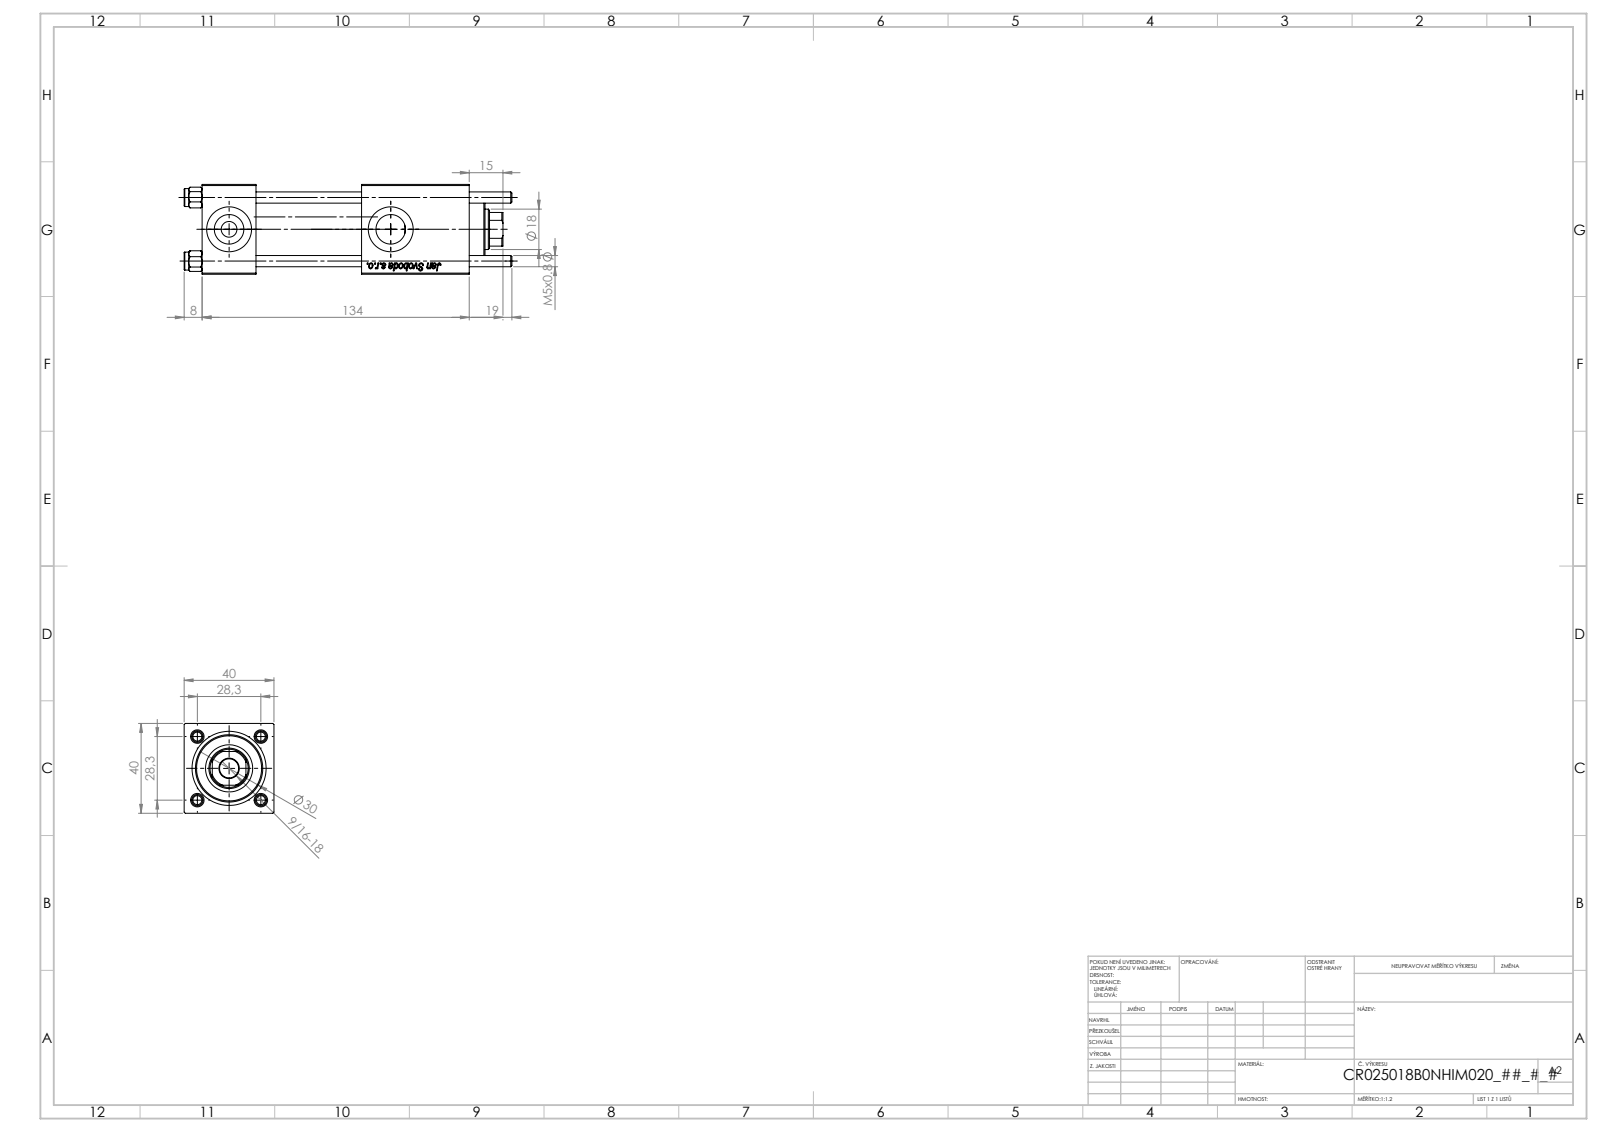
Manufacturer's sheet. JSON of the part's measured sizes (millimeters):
{"part_name": "V215CR_B_TYCINKA; V215CR_VCP_B; V215CR_B-1; NUT_M5_B (+1 more)", "step_written_by": "SolidWorks 2019 (CONFIG_CONTROL_DESIGN)", "units": "millimeters", "bodies": {"solids": 11, "faces": 1152, "planar": 428, "cylindrical": 76, "other": 648}, "overall_size": [146, 40, 40], "volume_mm3": 152491, "surface_area_mm2": 60895, "round_holes": [[5, 4], [20, 3], [7, 2], [13.16, 2], [8.5, 1], [18, 1], [21, 1], [25, 1], [30, 1]], "round_bosses_or_shafts": [[8, 4], [31, 1]], "partial_cylinders_radius": [[8.5, 1]], "face_to_face_distances": [40, 24, 71, 47, 90.3, 66.3, 19.3, 119, 95, 48], "hole_center_spacings": [20.01, 28.3, 40.02, 72]}
